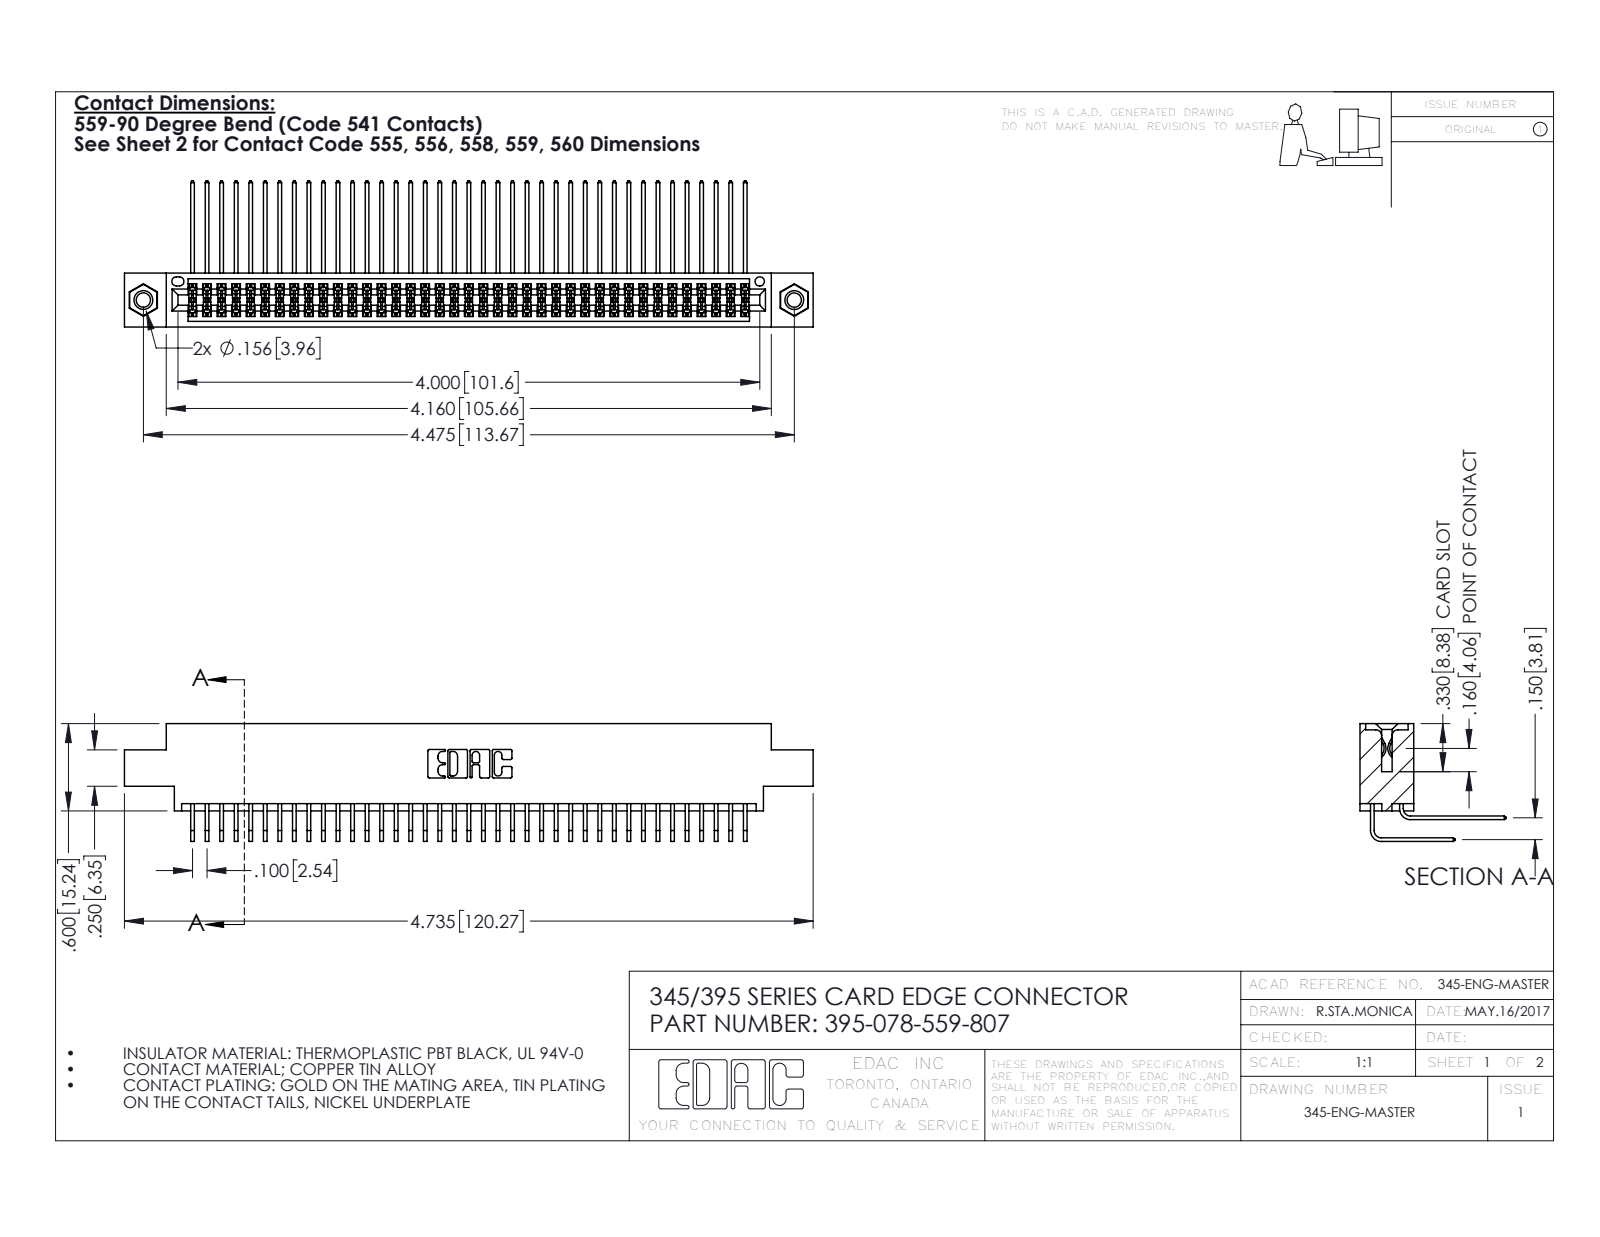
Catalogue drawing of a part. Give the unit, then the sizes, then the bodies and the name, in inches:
Units: inches
Overall size (bounding box): 4.735 × 1.005 × 0.809
Round holes (diameter × count): ⌀0.098 ×2, ⌀0.125 ×2, ⌀0.156 ×2, ⌀0.064 ×1
Round bosses / shafts (diameter × count): ⌀0.155 ×2
Partial cylindrical surfaces — rounded edges, fillets, slot ends (radius × count): R0.006 ×117, R0.01 ×22, R0.007 ×6, R0.031 ×6, R0.026 ×3, R0.014 ×2, R0.019 ×2, R0.022 ×2
Main face-to-face distances: 0.072, 0.298, 0.37, 0.2, 0.098, 0.272, 0.025, 0.225, 0.175, 0.15
Hole centre spacings: 0.27, 4.239, 4.475
Volume: 0.731 in³ · Surface area: 30.9 in²
Bodies: 81 solids, 4246 faces (2846 planar, 1384 cylindrical, 16 other)
Part name (STEP PRODUCT): 345-250-001_345-250-005-103; 345-292-001_558 559 Tail - 1; 345 Part_0.170 Offset - 0.156 Dia-TI; 395-078-559-807 (+1 more)
STEP written by: SolidWorks 2016 (CONFIG_CONTROL_DESIGN)
